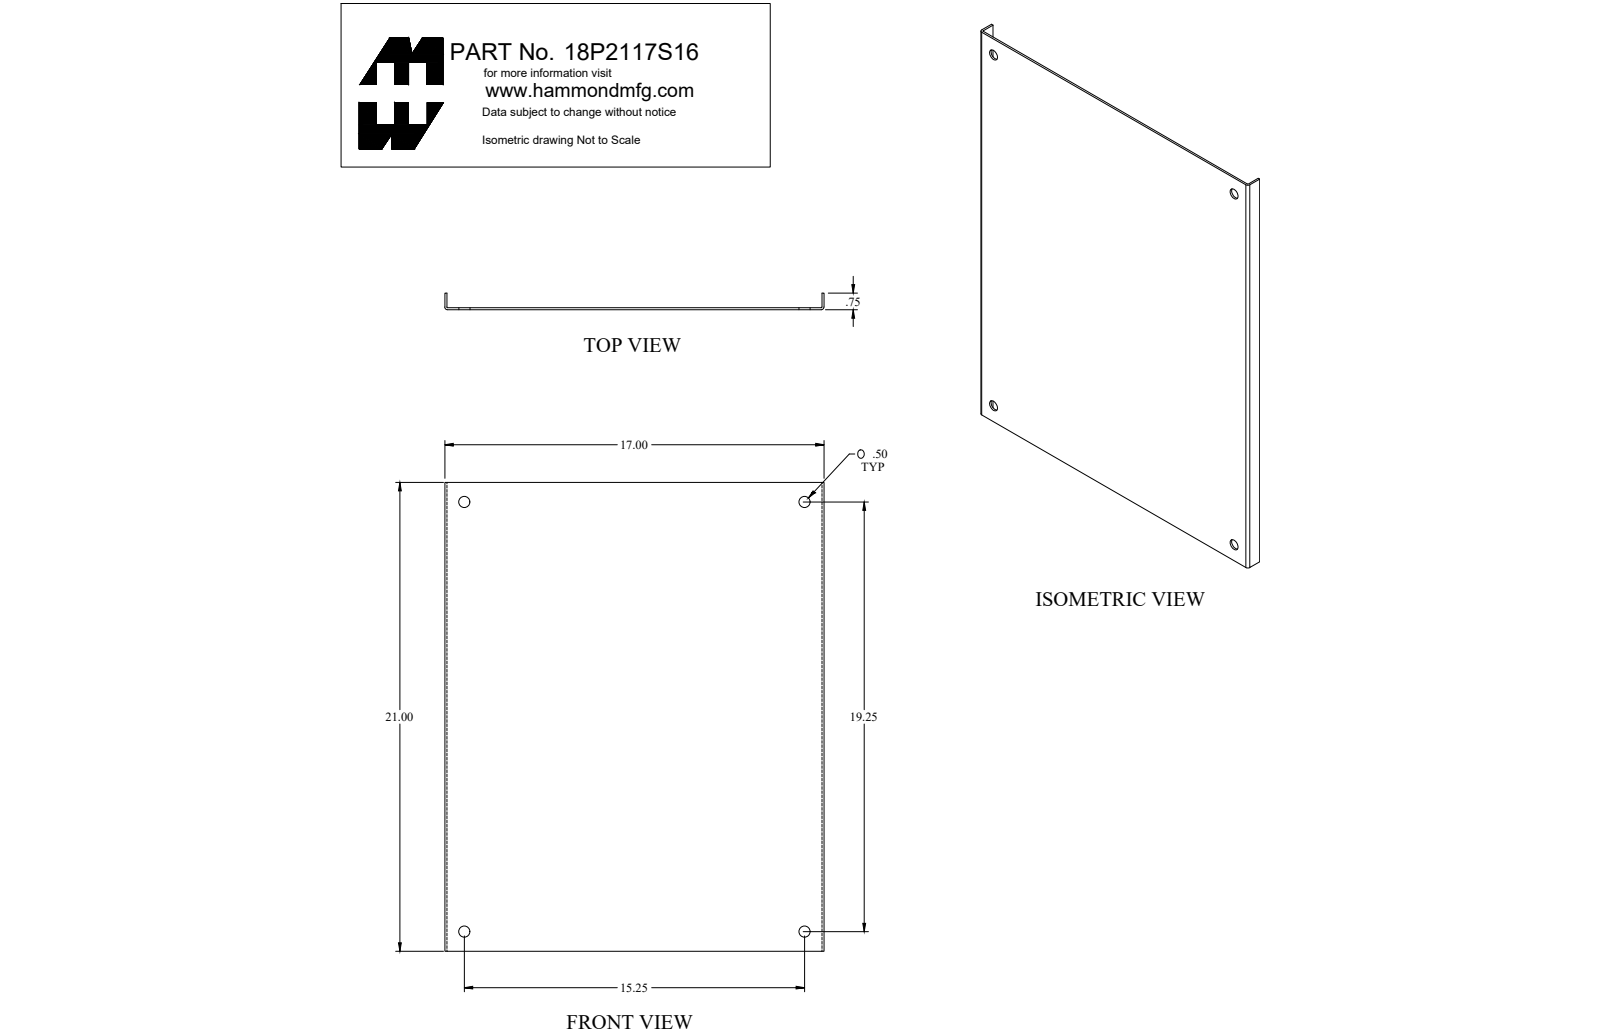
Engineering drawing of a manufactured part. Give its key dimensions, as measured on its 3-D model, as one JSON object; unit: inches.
{"part_name": "18P2117S16_Default", "step_written_by": "SolidWorks 2018 (CONFIG_CONTROL_DESIGN)", "units": "inches", "bodies": {"solids": 1, "faces": 22, "planar": 10, "cylindrical": 12, "other": 0}, "overall_size": [21, 17, 0.75], "volume_in3": 36.32, "surface_area_in2": 772.7, "round_holes": [[0.5, 4]], "partial_cylinders_radius": [[0.03, 2], [0.125, 2]], "face_to_face_distances": [0.095, 16.905, 17, 16.81, 0.75, 0.655, 21], "hole_center_spacings": [15.25, 19.25, 24.559]}
